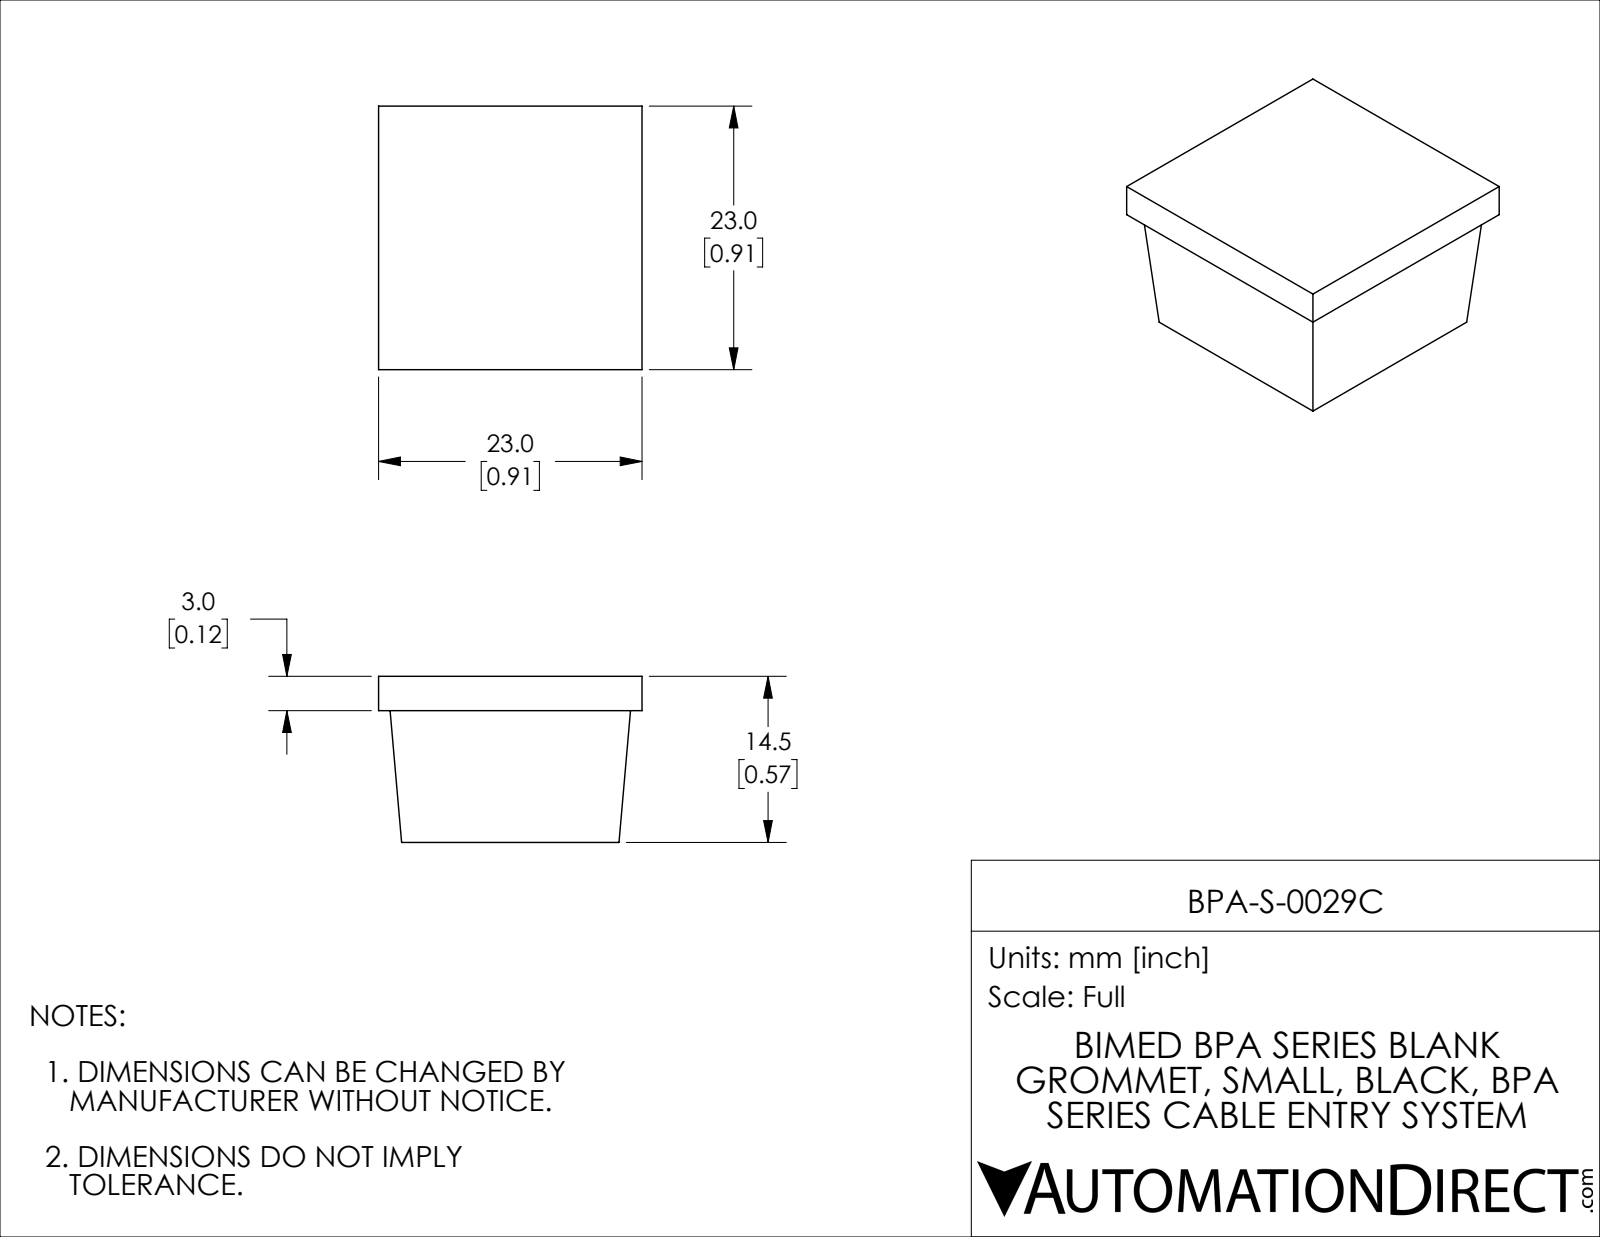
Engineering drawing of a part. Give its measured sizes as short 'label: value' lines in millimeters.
name: BPA-S-0029C
written by: SolidWorks 2021 (CONFIG_CONTROL_DESIGN)
unit: mm
bodies: 1 solid, 11 faces (11 planar, 0 cylindrical, 0 other)
size: 23 × 23 × 14.5
volume: 6 188 mm³; area: 2 177 mm²
face distances: 14.5, 23, 11.5, 3
